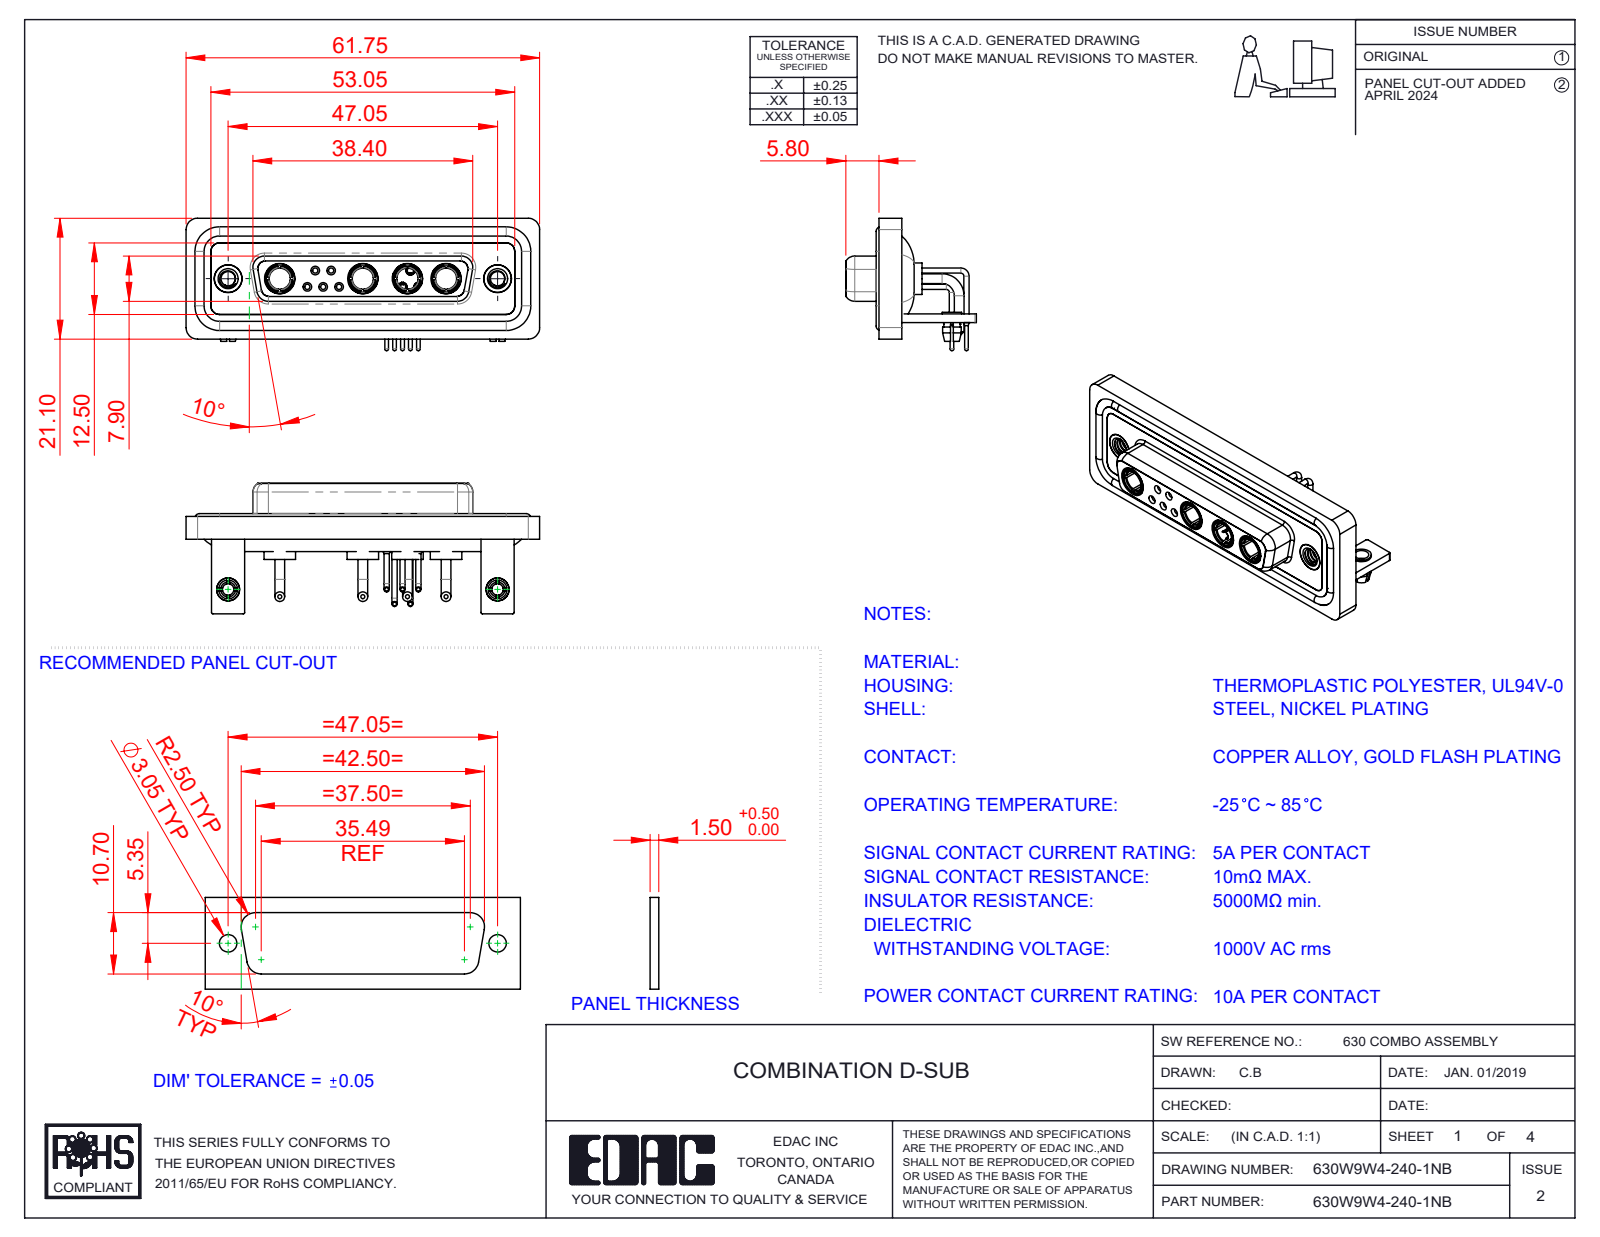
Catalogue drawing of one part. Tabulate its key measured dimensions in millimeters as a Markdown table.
| quantity | value |
| --- | --- |
| part name | 630Combo Stabilizer Bracket_50 Contacts; 630Combo Housing_9W4; 630Combo Contact Row 2_50 Contacts; 630Combo Board Lock_50 Contacts (+7 more) |
| STEP written by | SolidWorks 2023 (CONFIG_CONTROL_DESIGN) |
| units | millimeters |
| bodies | 24 solids, 1097 faces (364 planar, 457 cylindrical, 276 other) |
| overall size | 61.75 × 23.12 × 22.8 |
| volume | 8 616 mm³ |
| surface area | 14 793 mm² |
| round holes (diameter × count) | 2 × 7, 4.85 × 6, 0.9 × 5, 1.1 × 5, 1.5 × 5, 2.5 × 4, 3.7 × 4, 5.3 × 4, 1.6 × 3, 1.7 × 2, 3.2 × 2, 4 × 2 |
| round bosses / shafts (diameter × count) | 0.9 × 10, 1.6 × 9, 1.7 × 8, 2 × 5, 1.5 × 5, 0.65 × 5, 5.5 × 4, 5.2 × 4 |
| partial cylindrical surfaces (radius × count) | 2 × 19, 1.5 × 18, 0.25 × 16, 1.35 × 8, 1.6 × 8, 0.5 × 5, 0.6 × 4, 0.65 × 4 |
| main face-to-face distances | 0.4, 1.8, 2.9, 1.5, 3.7, 4.1, 1.1, 1.4, 1.6, 2.5 |
| hole center spacings | 3.16, 2.77, 5.04, 13.85, 11.08, 12.79, 15.5, 5.54 |
